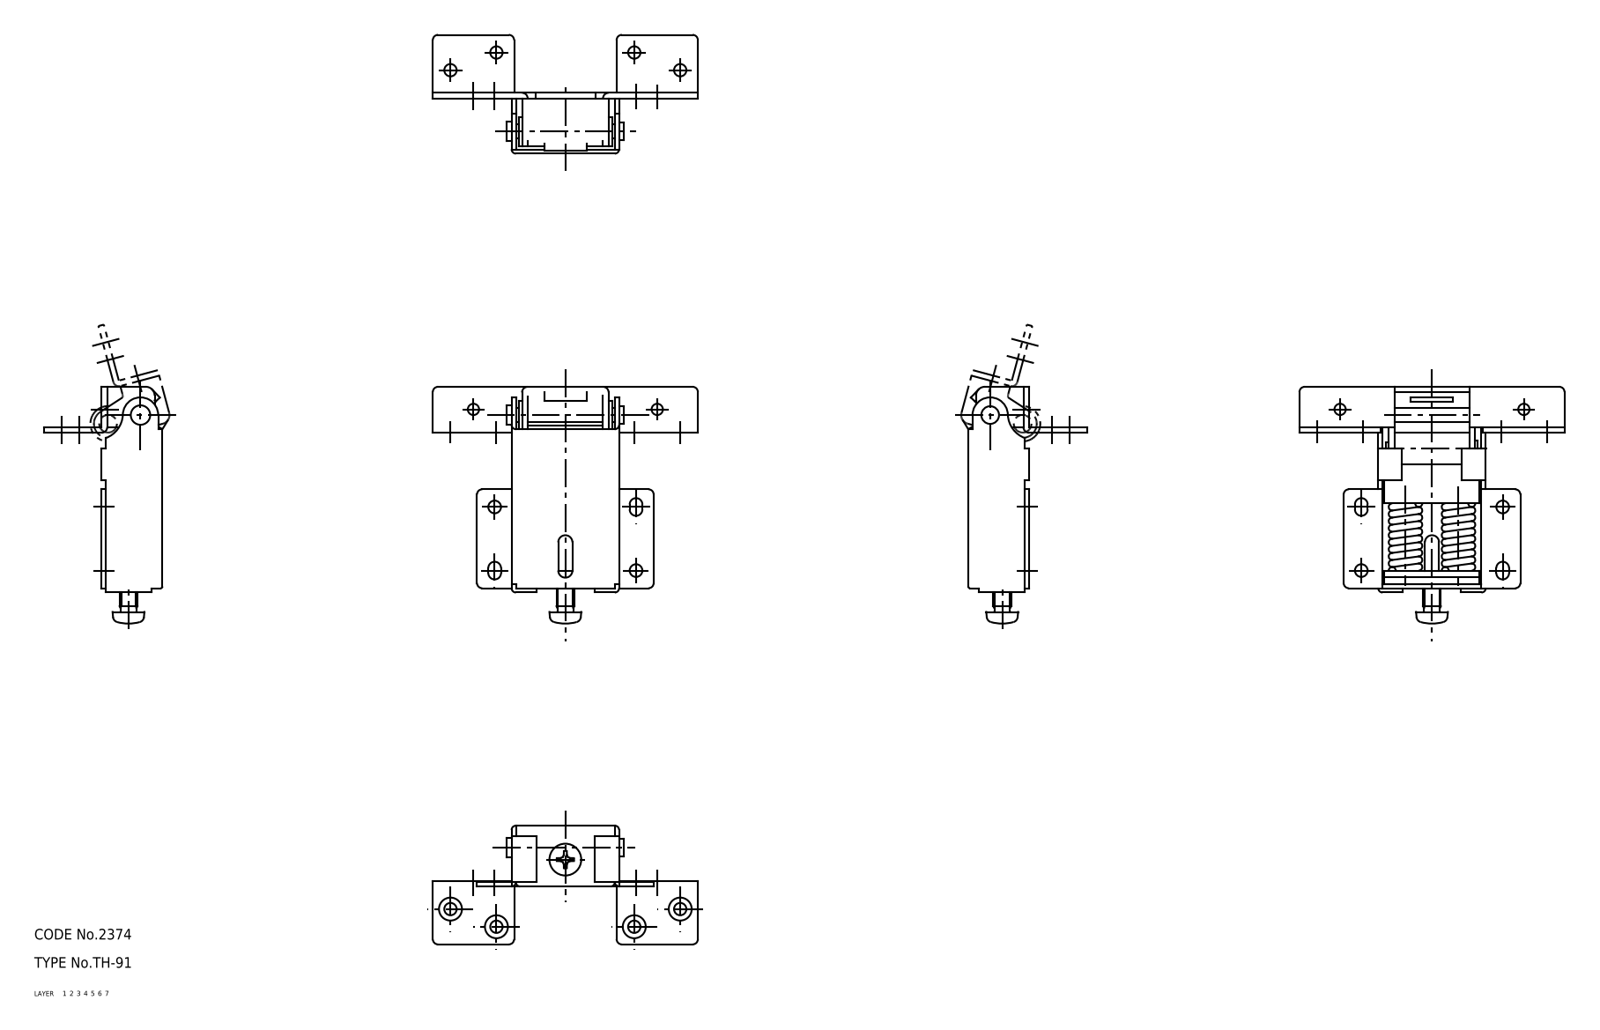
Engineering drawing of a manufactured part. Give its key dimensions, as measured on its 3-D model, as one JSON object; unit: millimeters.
{"part_name": "roller; shaft_A; spring holder_A; TH_91 (+8 more)", "step_written_by": "SolidWorks 2015 (AUTOMOTIVE_DESIGN)", "units": "millimeters", "bodies": {"solids": 13, "faces": 284, "planar": 141, "cylindrical": 117, "other": 26}, "overall_size": [75, 67, 33.6], "volume_mm3": 16034, "surface_area_mm2": 22146, "round_holes": [[3.5, 4], [3.2, 2], [3.6, 2], [9.5, 2], [3.1, 1], [4, 1], [4.1, 1], [4.48, 1], [5, 1]], "round_bosses_or_shafts": [[5, 2], [9, 1], [8, 1], [5.5, 1], [3, 1]], "partial_cylinders_radius": [[1.2, 9], [2, 8], [0.5, 4], [1.5, 4], [1.8, 4], [1.6, 3], [5, 2], [2.4, 1]], "face_to_face_distances": [1.2, 1.6, 16, 29.2, 17.2, 28, 2, 30.4, 44.4, 42.4], "hole_center_spacings": [7.6, 13.93, 23.5, 27.23, 29.26, 33.72, 35.39, 42.79]}
